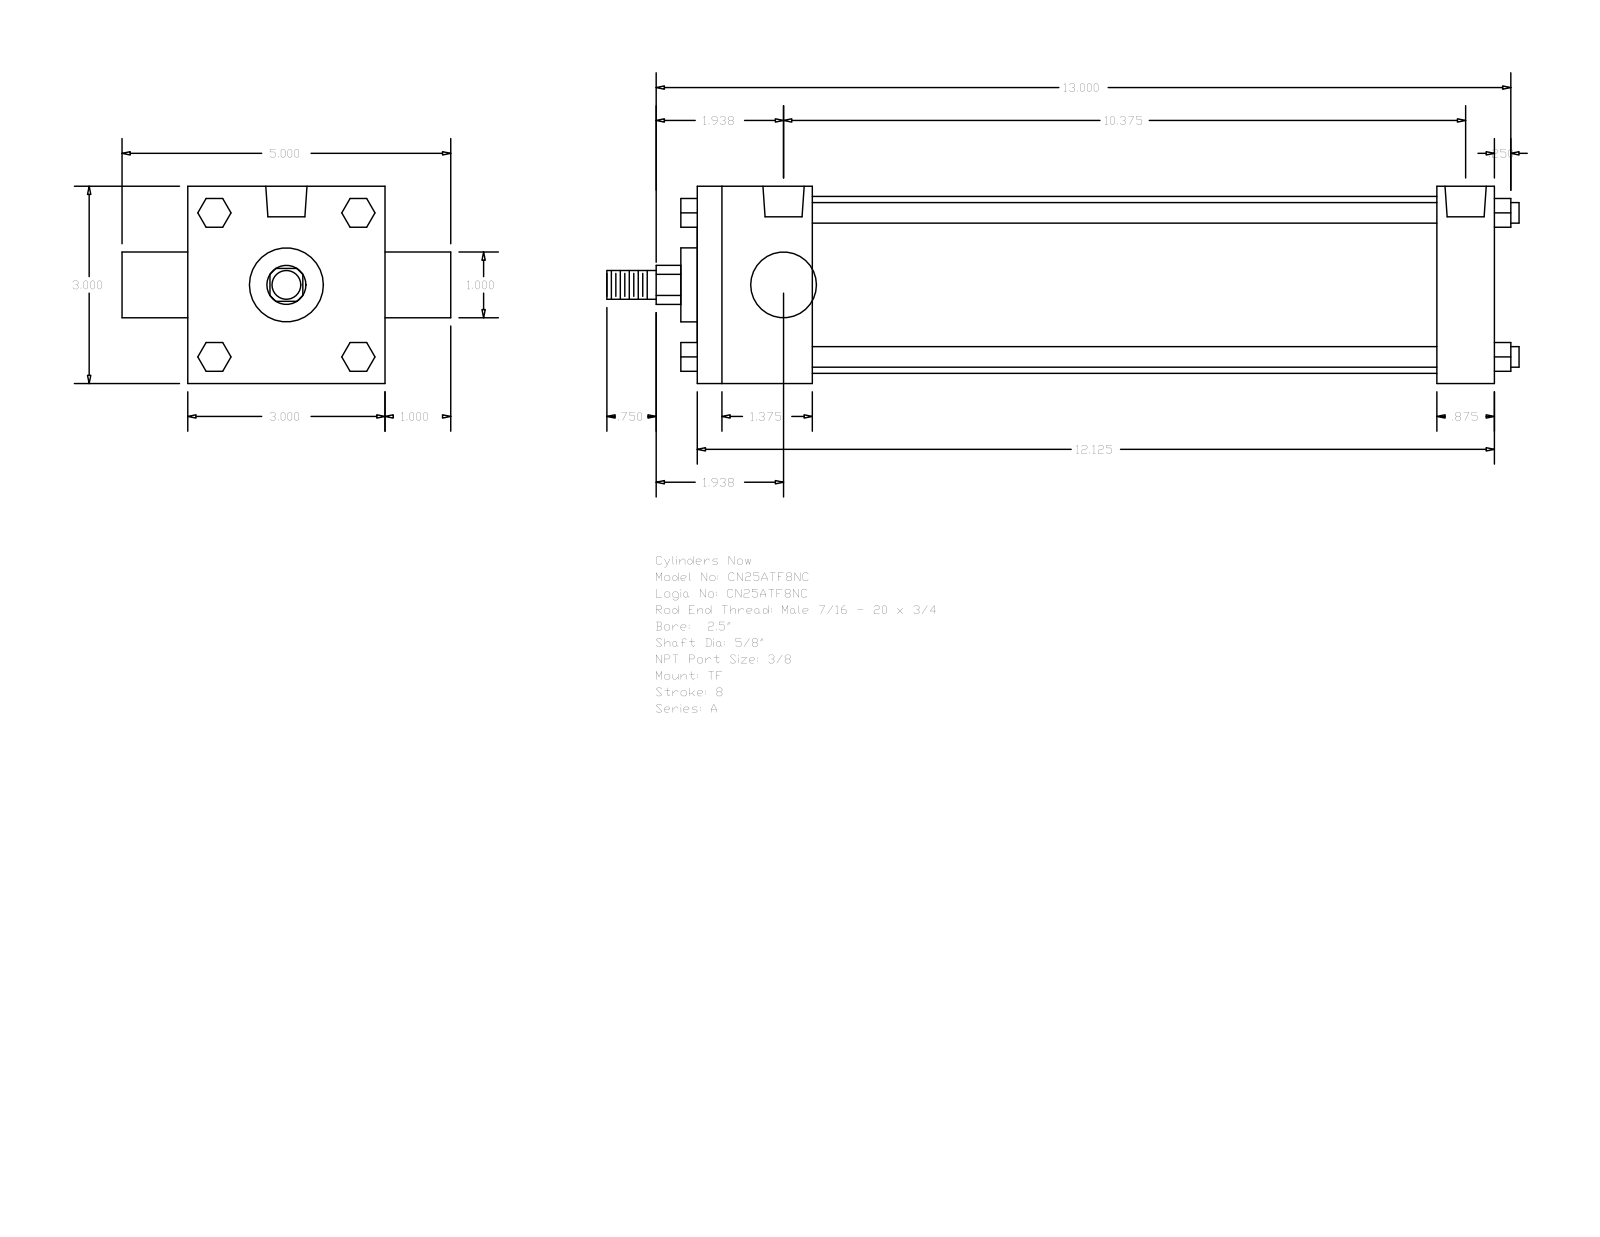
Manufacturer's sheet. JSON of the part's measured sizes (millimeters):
{"part_name": "A_TF__0250_0.625", "step_written_by": "GSSL Pune (CONFIG_CONTROL_DESIGN)", "units": "millimeters", "bodies": {"solids": 0, "faces": 120, "planar": 92, "cylindrical": 28, "other": 0}, "overall_size": [352.43, 127, 76.2], "round_holes": [[5.56, 3], [15.93, 2]], "round_bosses_or_shafts": [[7.94, 4], [68.33, 1], [28.57, 1], [25.4, 1], [15.88, 1], [11.11, 1]], "partial_cylinders_radius": [[7.54, 1]], "face_to_face_distances": [76.2, 307.97, 44.45, 285.74, 241.29, 263.52, 22.23, 25.4, 101.6, 6.35], "hole_center_spacings": [2.38, 265.91, 263.53, 268.29]}
